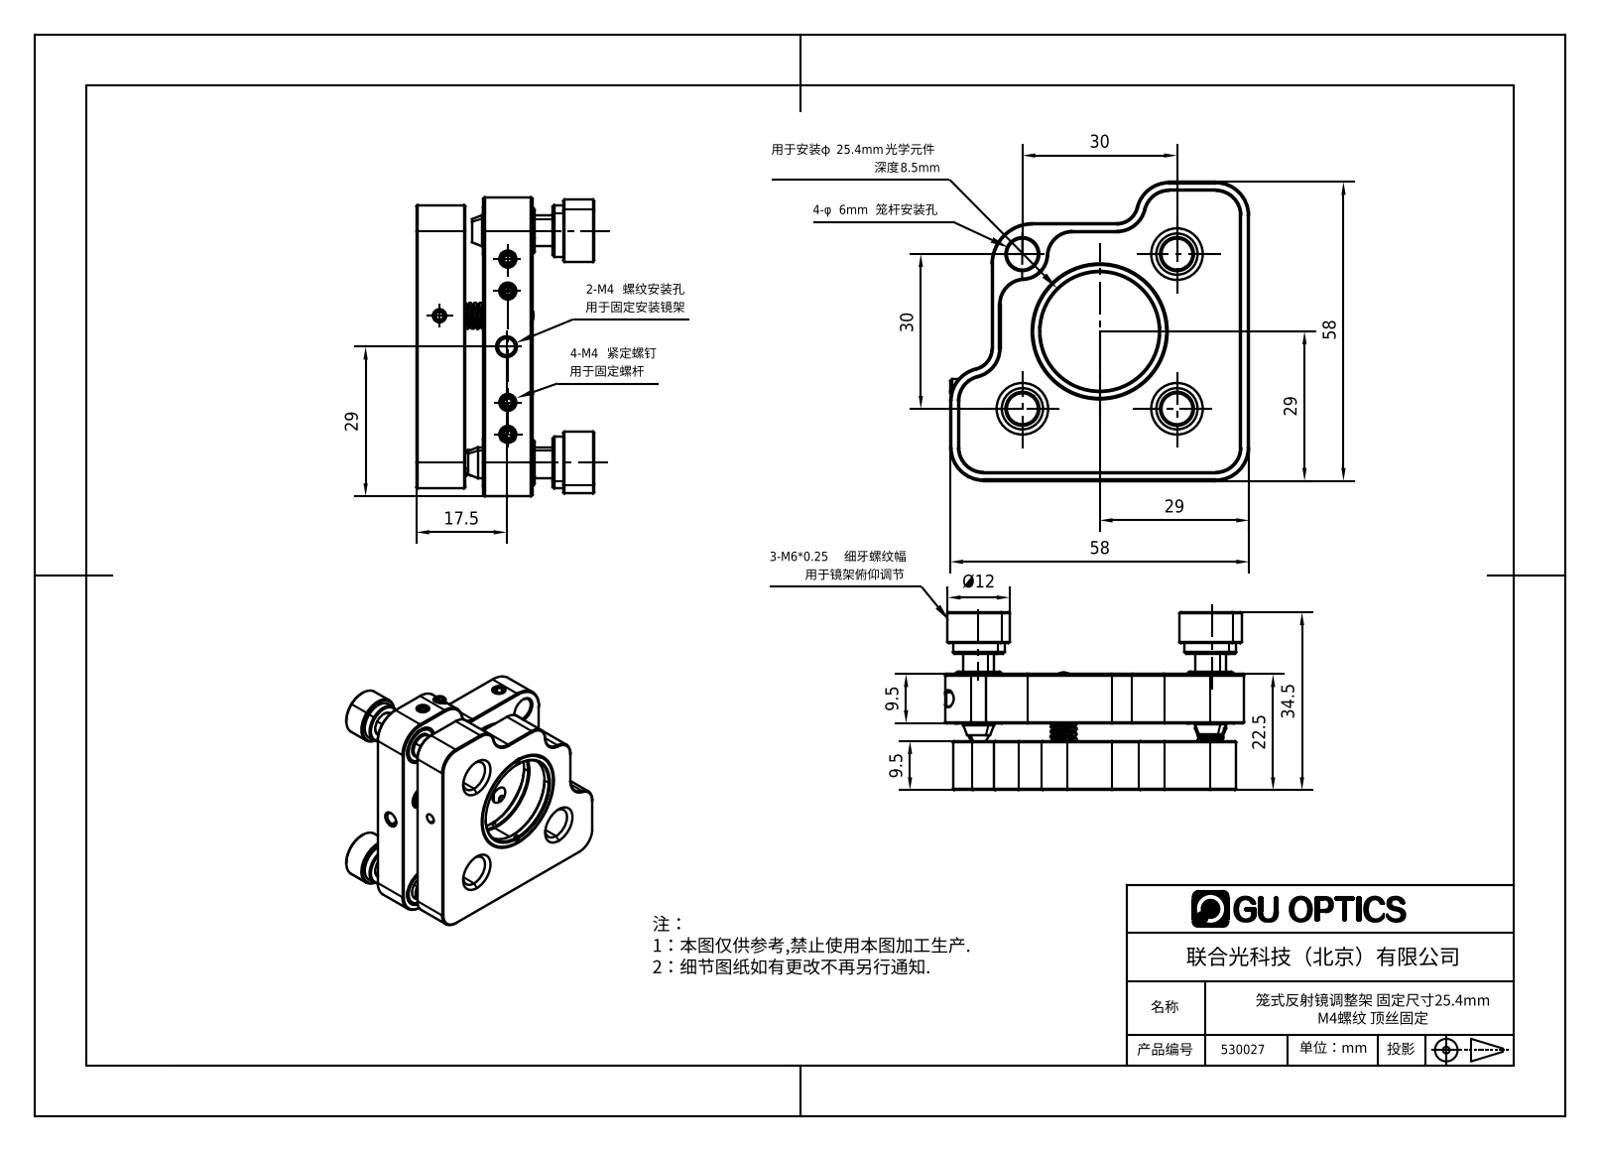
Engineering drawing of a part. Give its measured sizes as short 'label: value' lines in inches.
written by: SolidWorks 2018 (AUTOMOTIVE_DESIGN)
unit: in
bodies: 0 solids, 490 faces (144 planar, 140 cylindrical, 206 other)
size: 2.283 × 2.283 × 1.358
holes: 7× ⌀0.13, 6× ⌀0.236, 3× ⌀0.157, 3× ⌀0.315, 1× ⌀0.098, 1× ⌀0.921, 1× ⌀1.039, 1× ⌀1.299
bosses: 3× ⌀0.472, 3× ⌀0.394, 3× ⌀0.374, 3× ⌀0.339, 3× ⌀0.236, 2× ⌀0.079, 2× ⌀0.059, 1× ⌀0.157
rounds: 8× R0.197, 5× R0.256, 4× R0.04, 2× R0.031, 2× R0.098, 2× R0.157, 2× R0.217, 1× R0.187
face distances: 0.374, 0.512, 0.138, 0.886, 0.059, 0.315, 1.909, 2.224, 1.969, 0.472
hole spacings: 1.506, 0.835, 1.181, 0.418, 1.253, 2.088, 0.244, 0.425
